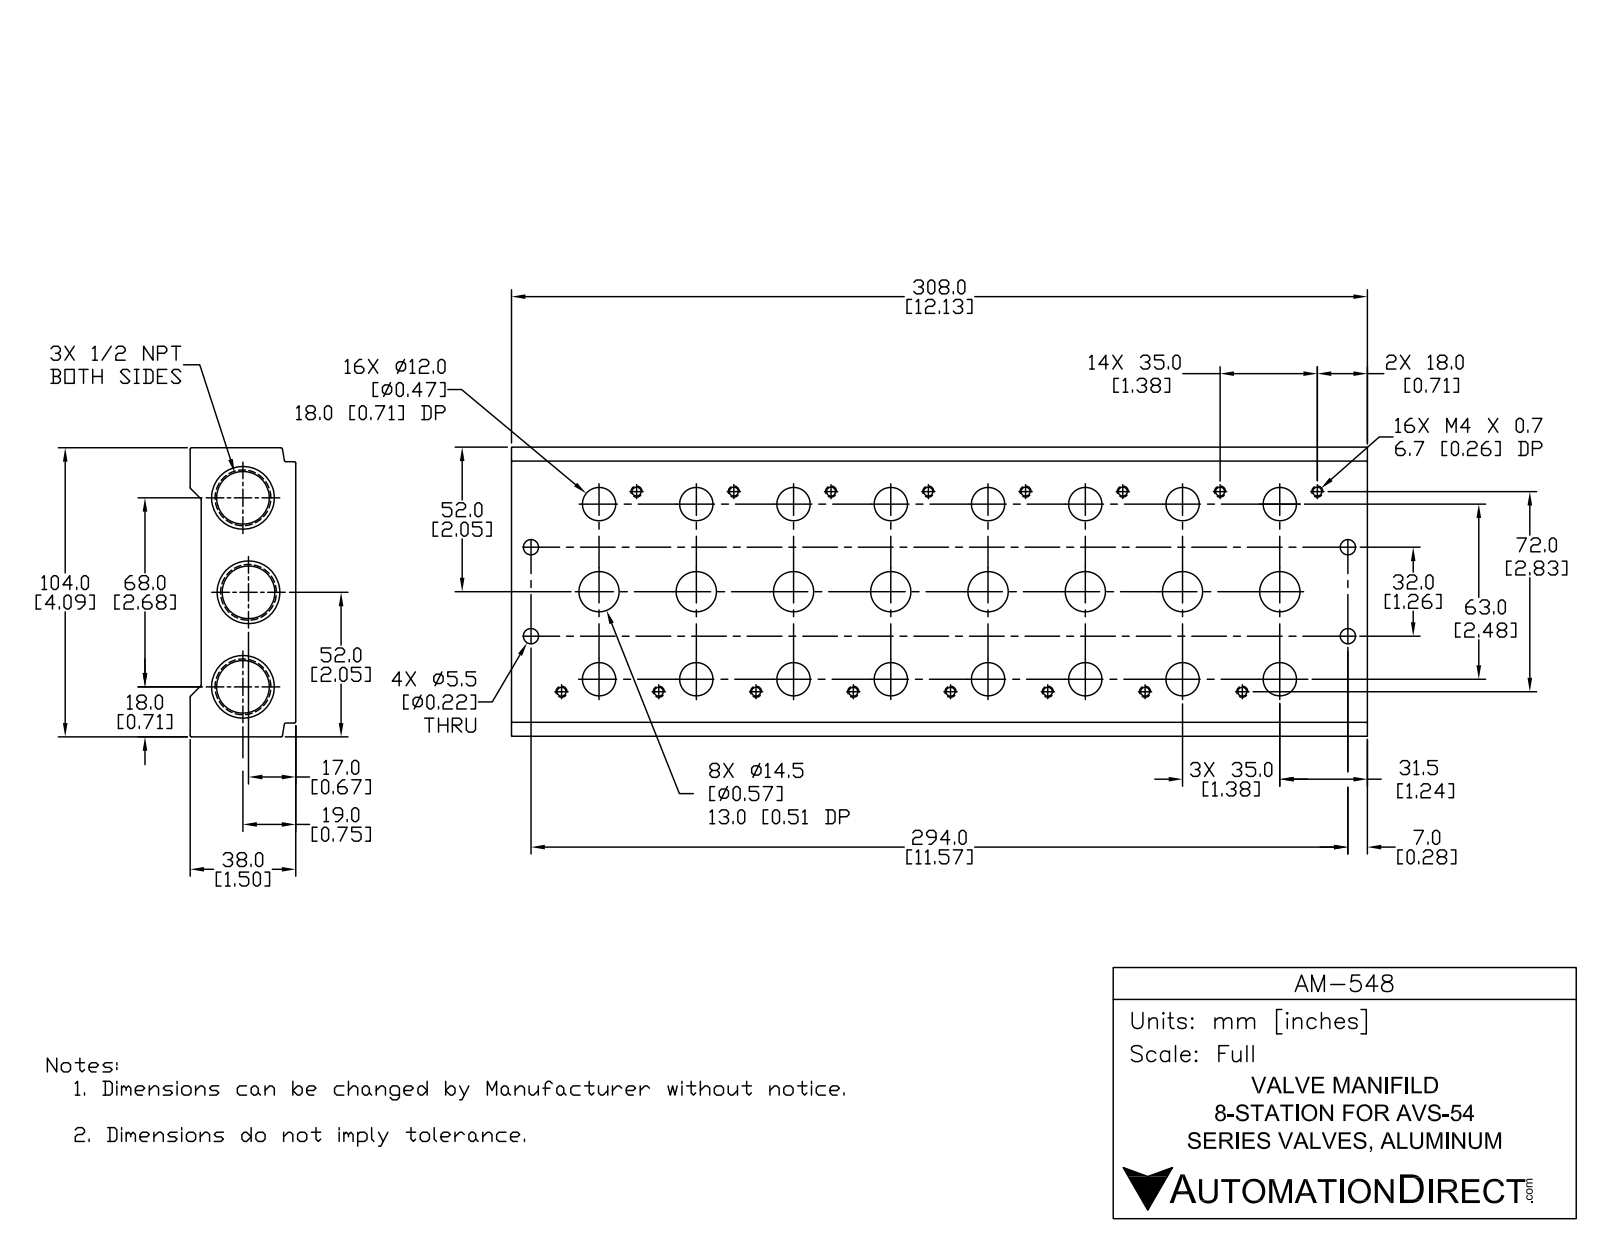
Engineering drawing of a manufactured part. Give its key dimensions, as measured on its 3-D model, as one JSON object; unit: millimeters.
{"part_name": "AM-548", "step_written_by": "SolidWorks 2015 (CONFIG_CONTROL_DESIGN)", "units": "millimeters", "bodies": {"solids": 1, "faces": 201, "planar": 52, "cylindrical": 105, "other": 44}, "overall_size": [308, 104, 38], "volume_mm3": 884796, "surface_area_mm2": 154290, "round_holes": [[3.3, 16], [8.5, 16], [13, 8], [5.5, 4], [17.86, 3]], "partial_cylinders_radius": [[0.5, 11]], "face_to_face_distances": [38, 4, 34, 104, 308, 28, 24, 10, 6, 98], "hole_center_spacings": [35, 70, 14.23, 68.84, 105, 140, 175, 21.97]}
